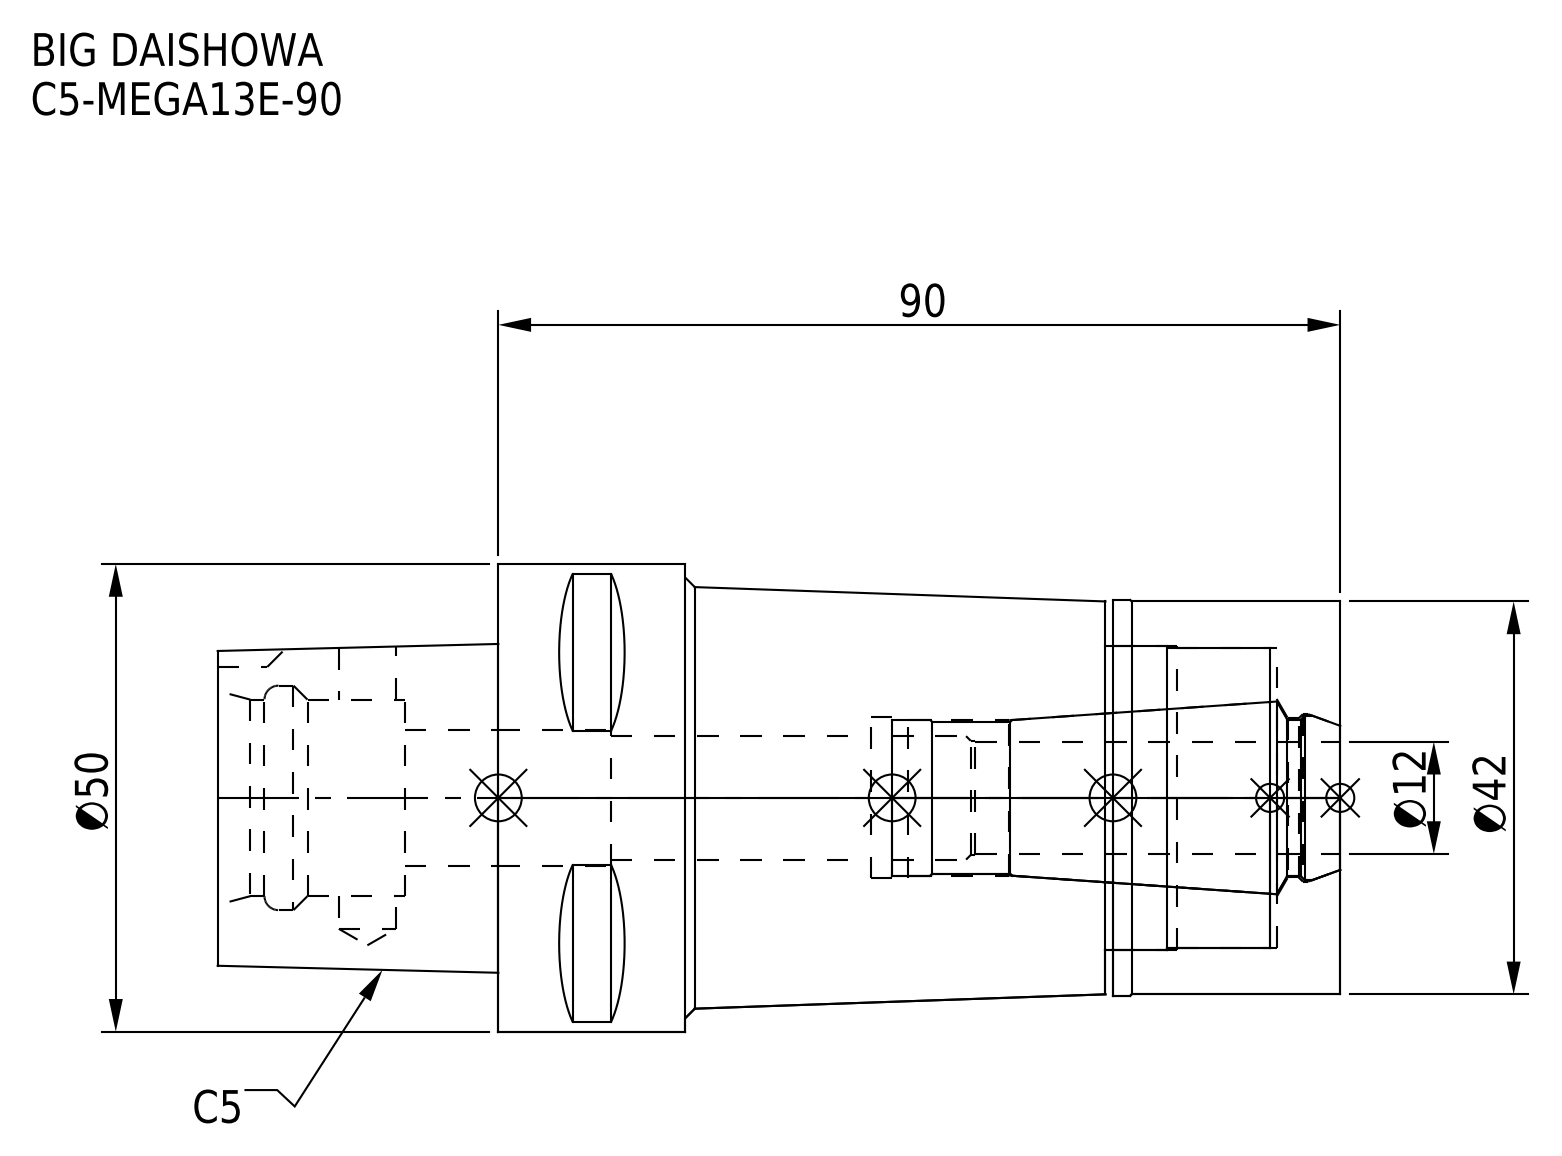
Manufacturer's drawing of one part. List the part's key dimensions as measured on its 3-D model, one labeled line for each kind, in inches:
Part name (STEP PRODUCT): MEN13_1.stp; C5-MEGA13E-90-120_ASM.stp; C5-MEGA13E-90-120.stp; C5-MEGA13E-90-120-FreeParts (+3 more)
STEP written by: SolidWorks 2019 (CONFIG_CONTROL_DESIGN)
Units: inches
Bodies: 2 solids, 97 faces (36 planar, 37 cylindrical, 24 other)
Overall size (bounding box): 4.724 × 1.969 × 1.969
Volume: 8.483 in³ · Surface area: 48.86 in²
Round holes (diameter × count): ⌀0.24 ×1, ⌀0.524 ×1, ⌀0.571 ×1, ⌀0.654 ×1, ⌀0.669 ×1, ⌀0.677 ×1, ⌀0.705 ×1, ⌀0.827 ×1, ⌀0.945 ×1, ⌀1.26 ×1, ⌀1.28 ×1
Round bosses / shafts (diameter × count): ⌀1.969 ×1, ⌀1.665 ×1, ⌀1.654 ×1
Partial cylindrical surfaces — rounded edges, fillets, slot ends (radius × count): R0.157 ×1
Main face-to-face distances: 3.543, 0.988, 0.957, 2.587, 1.181, 0.031, 2.555, 3.248, 0.268, 0.689
